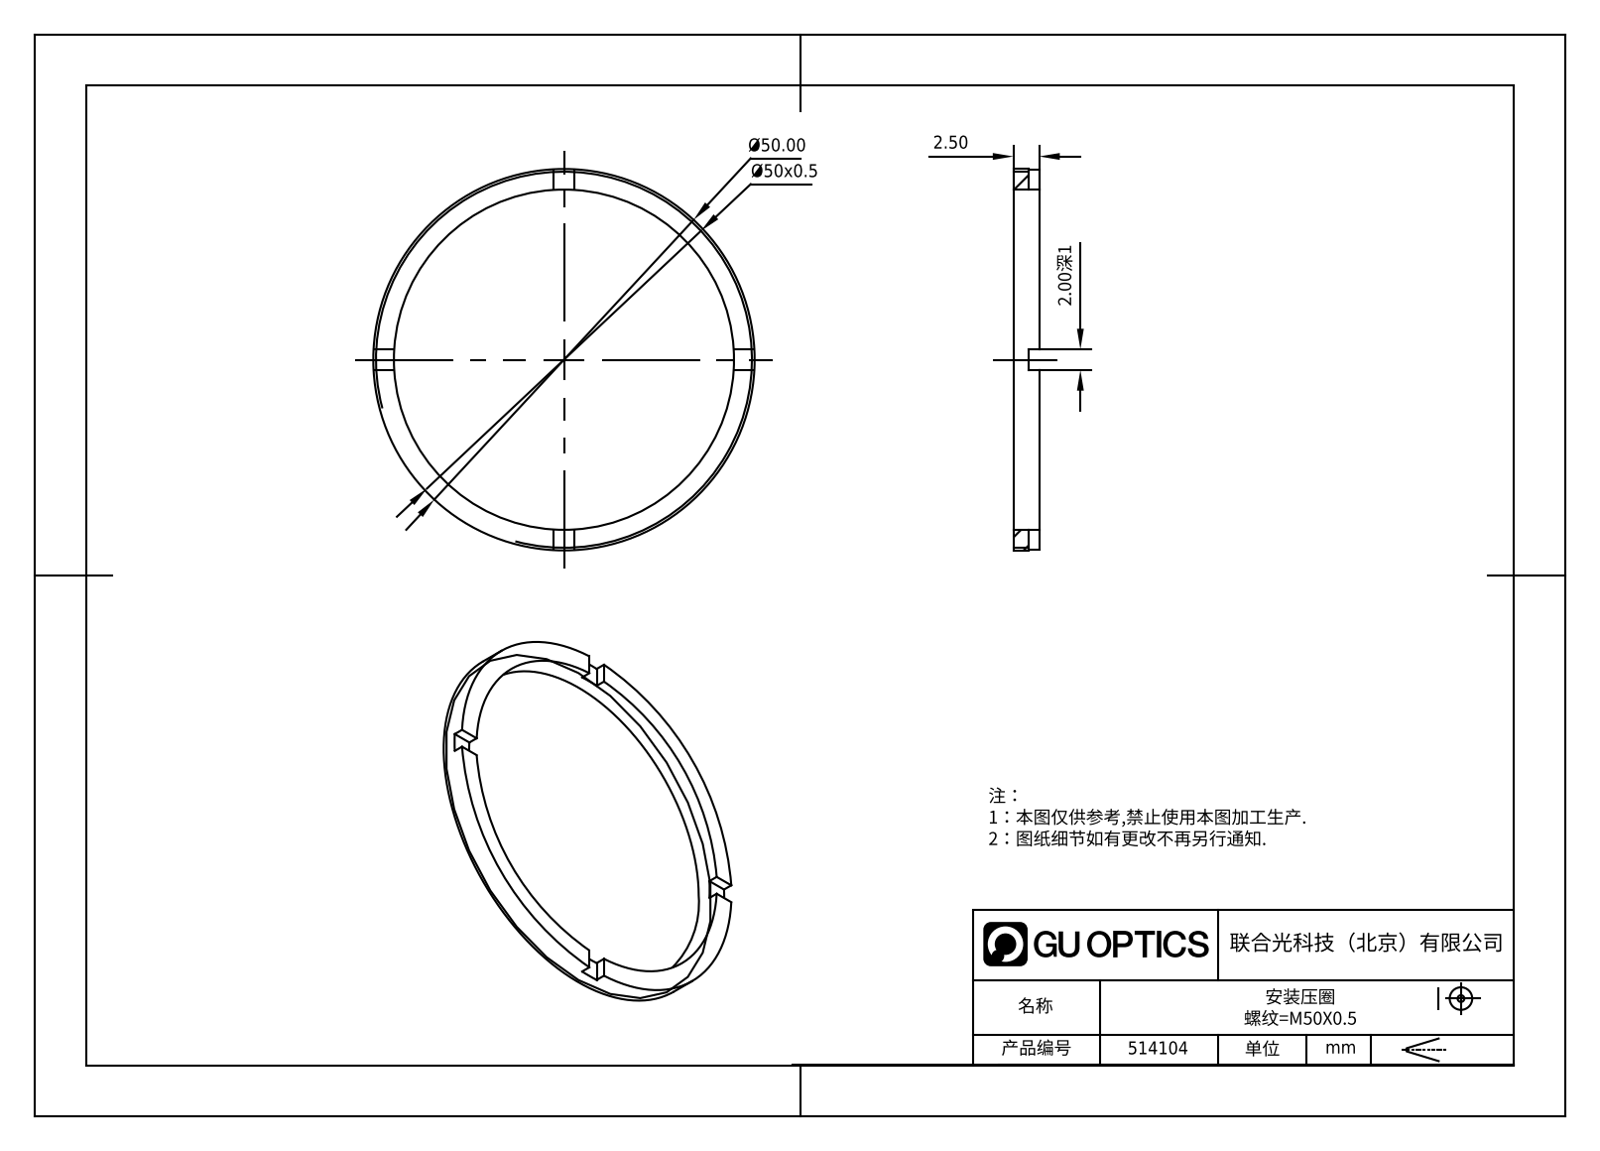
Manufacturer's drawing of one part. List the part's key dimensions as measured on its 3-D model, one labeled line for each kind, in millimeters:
Part name (STEP PRODUCT): 514104
STEP written by: SolidWorks 2020 (CONFIG_CONTROL_DESIGN)
Units: millimetres
Bodies: 1 solid, 21 faces (17 planar, 4 cylindrical, 0 other)
Overall size (bounding box): 50 × 50 × 2.5
Volume: 913 mm³ · Surface area: 1 496 mm²
Round holes (diameter × count): ⌀45 ×1
Round bosses / shafts (diameter × count): ⌀50 ×1
Main face-to-face distances: 2.5, 1.5, 1, 2
